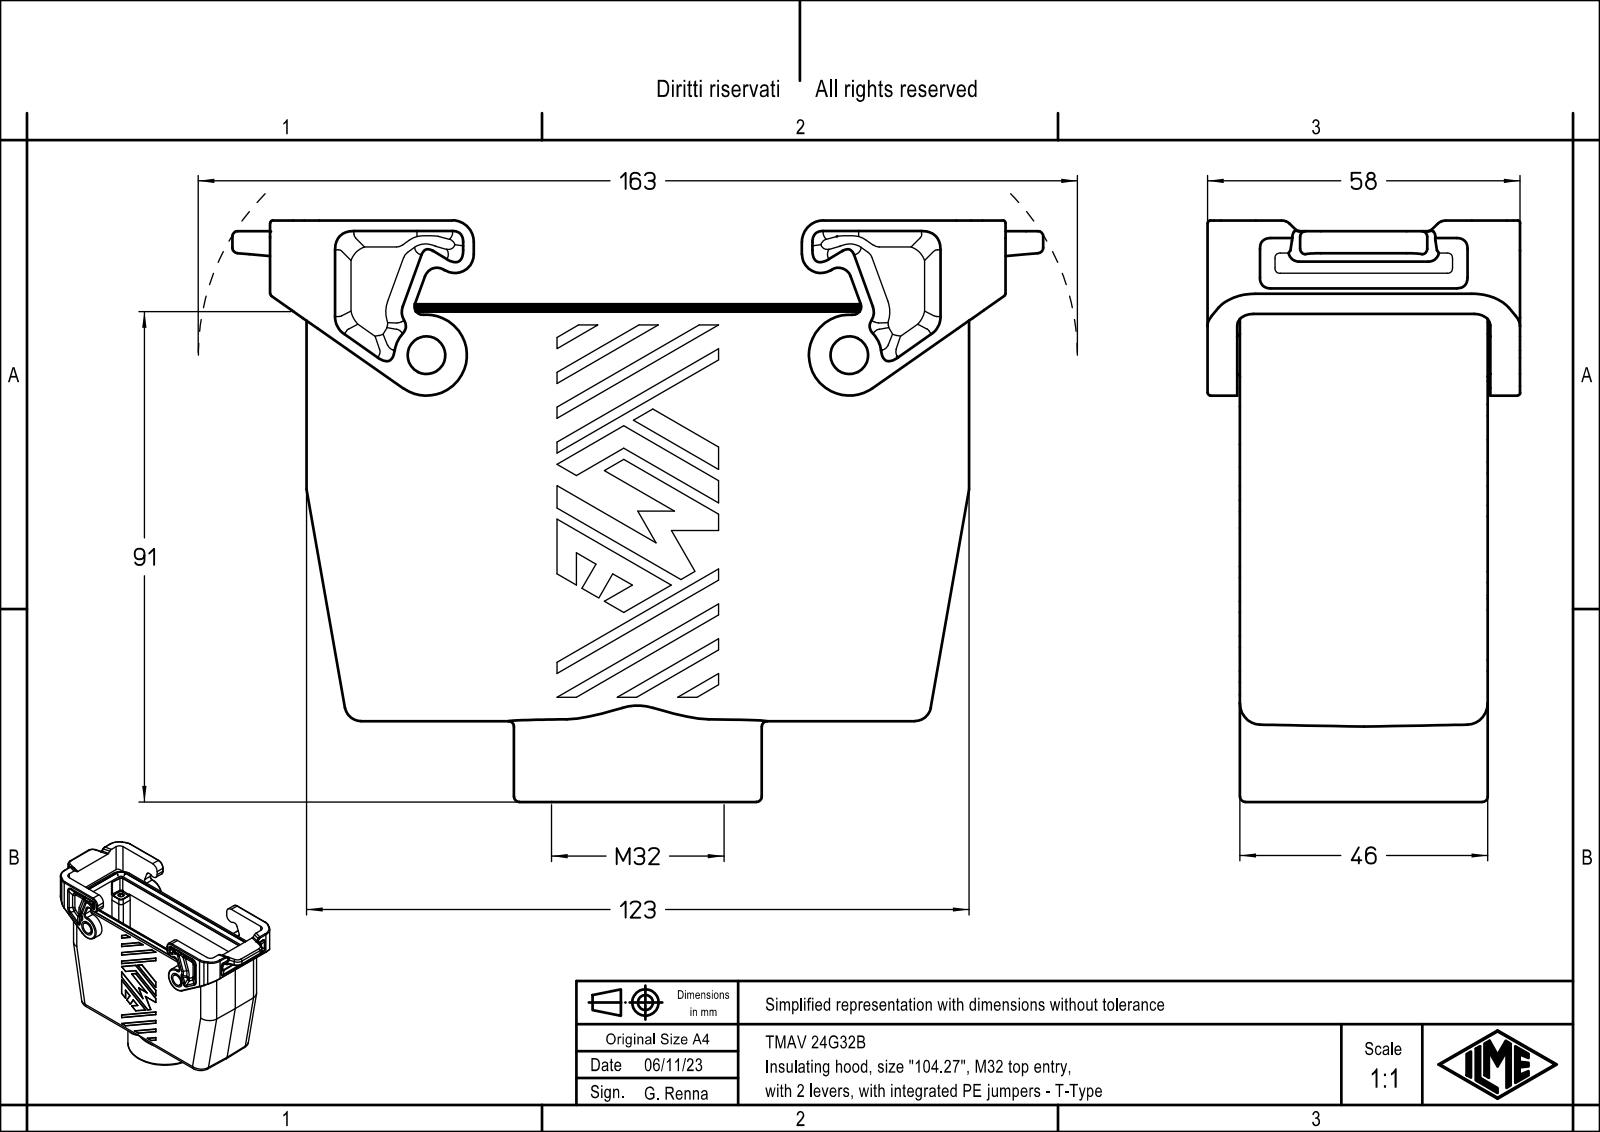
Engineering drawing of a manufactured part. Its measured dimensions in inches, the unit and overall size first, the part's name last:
Units: inches
Overall size (bounding box): 5.925 × 4.248 × 2.283
Round holes (diameter × count): ⌀0.138 ×4, ⌀1.102 ×1, ⌀1.205 ×1
Round bosses / shafts (diameter × count): ⌀0.276 ×2, ⌀1.811 ×1
Partial cylindrical surfaces — rounded edges, fillets, slot ends (radius × count): R0.006 ×88, R0.079 ×20, R0.118 ×20, R0.059 ×18, R0.039 ×16, R0.051 ×12, R0.236 ×8, R0.276 ×8
Main face-to-face distances: 0.213, 1.598, 1.386, 1.811, 0.232, 0.02, 1.618, 1.831, 1.37, 0.26
Hole centre spacings: 2.115, 1.063, 4.094, 4.23
Volume: 11.5 in³ · Surface area: 117.5 in²
Bodies: 1 solid, 754 faces (374 planar, 318 cylindrical, 62 other)
Part name (STEP PRODUCT): TMAV 24G32B
STEP written by: Creo Elements/Direct Modeling 20.1B 02-Apr-2019 (C) Parametric Technology GmbH (AUTOMOTIVE_DESIGN)
